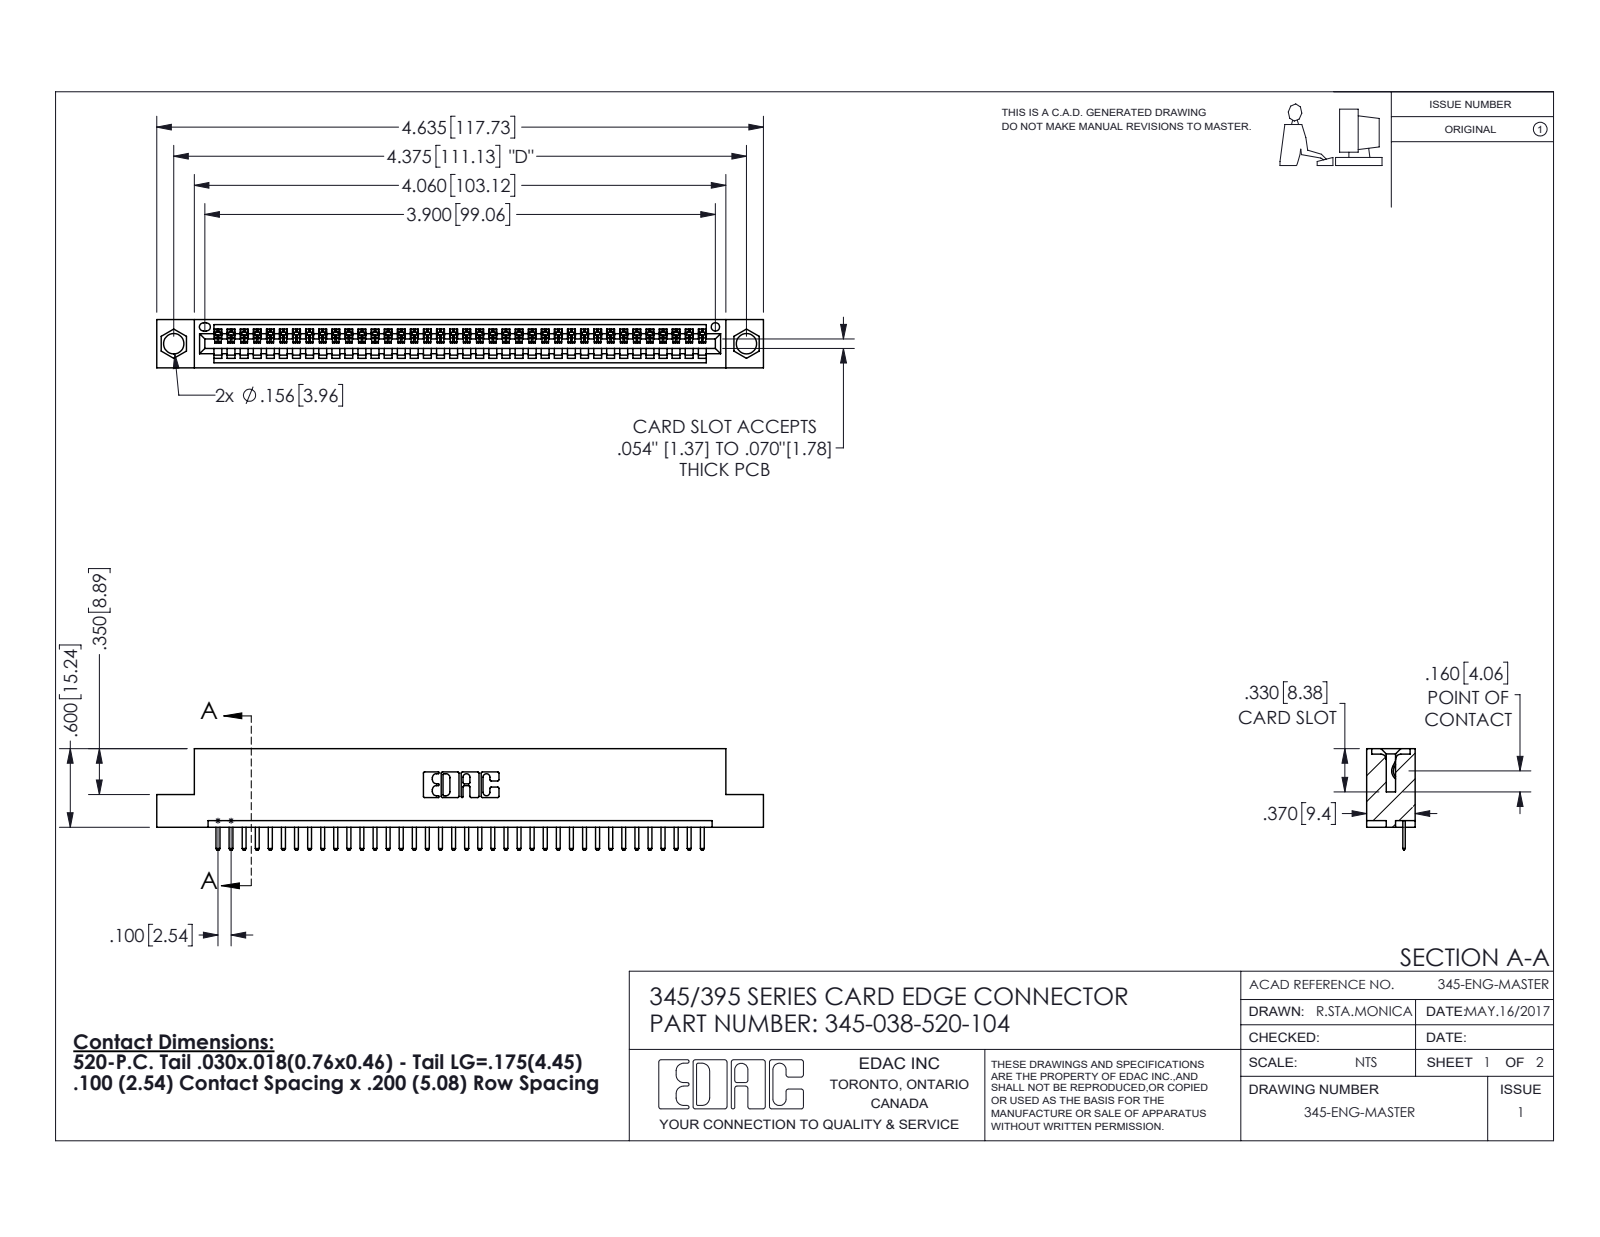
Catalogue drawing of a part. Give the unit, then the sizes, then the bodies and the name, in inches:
Units: inches
Overall size (bounding box): 4.635 × 0.775 × 0.37
Round holes (diameter × count): ⌀0.156 ×2, ⌀0.064 ×1
Partial cylindrical surfaces — rounded edges, fillets, slot ends (radius × count): R0.01 ×78, R0.006 ×76, R0.01 ×22, R0.007 ×6, R0.031 ×6, R0.026 ×3, R0.031 ×2, R0.04 ×2
Main face-to-face distances: 0.298, 0.072, 0.37, 0.2, 0.098, 0.272, 0.025, 0.225, 0.072, 0.149
Hole centre spacings: 0.27, 4.139, 4.375
Volume: 0.668 in³ · Surface area: 21.62 in²
Bodies: 39 solids, 2482 faces (1676 planar, 806 cylindrical, 0 other)
Part name (STEP PRODUCT): 345-038-520-104; 345 Part_Flush Mounting Lugs - 0.156 Dia-TH; 345-292-001_345-293-120
STEP written by: SolidWorks 2016 (CONFIG_CONTROL_DESIGN)
